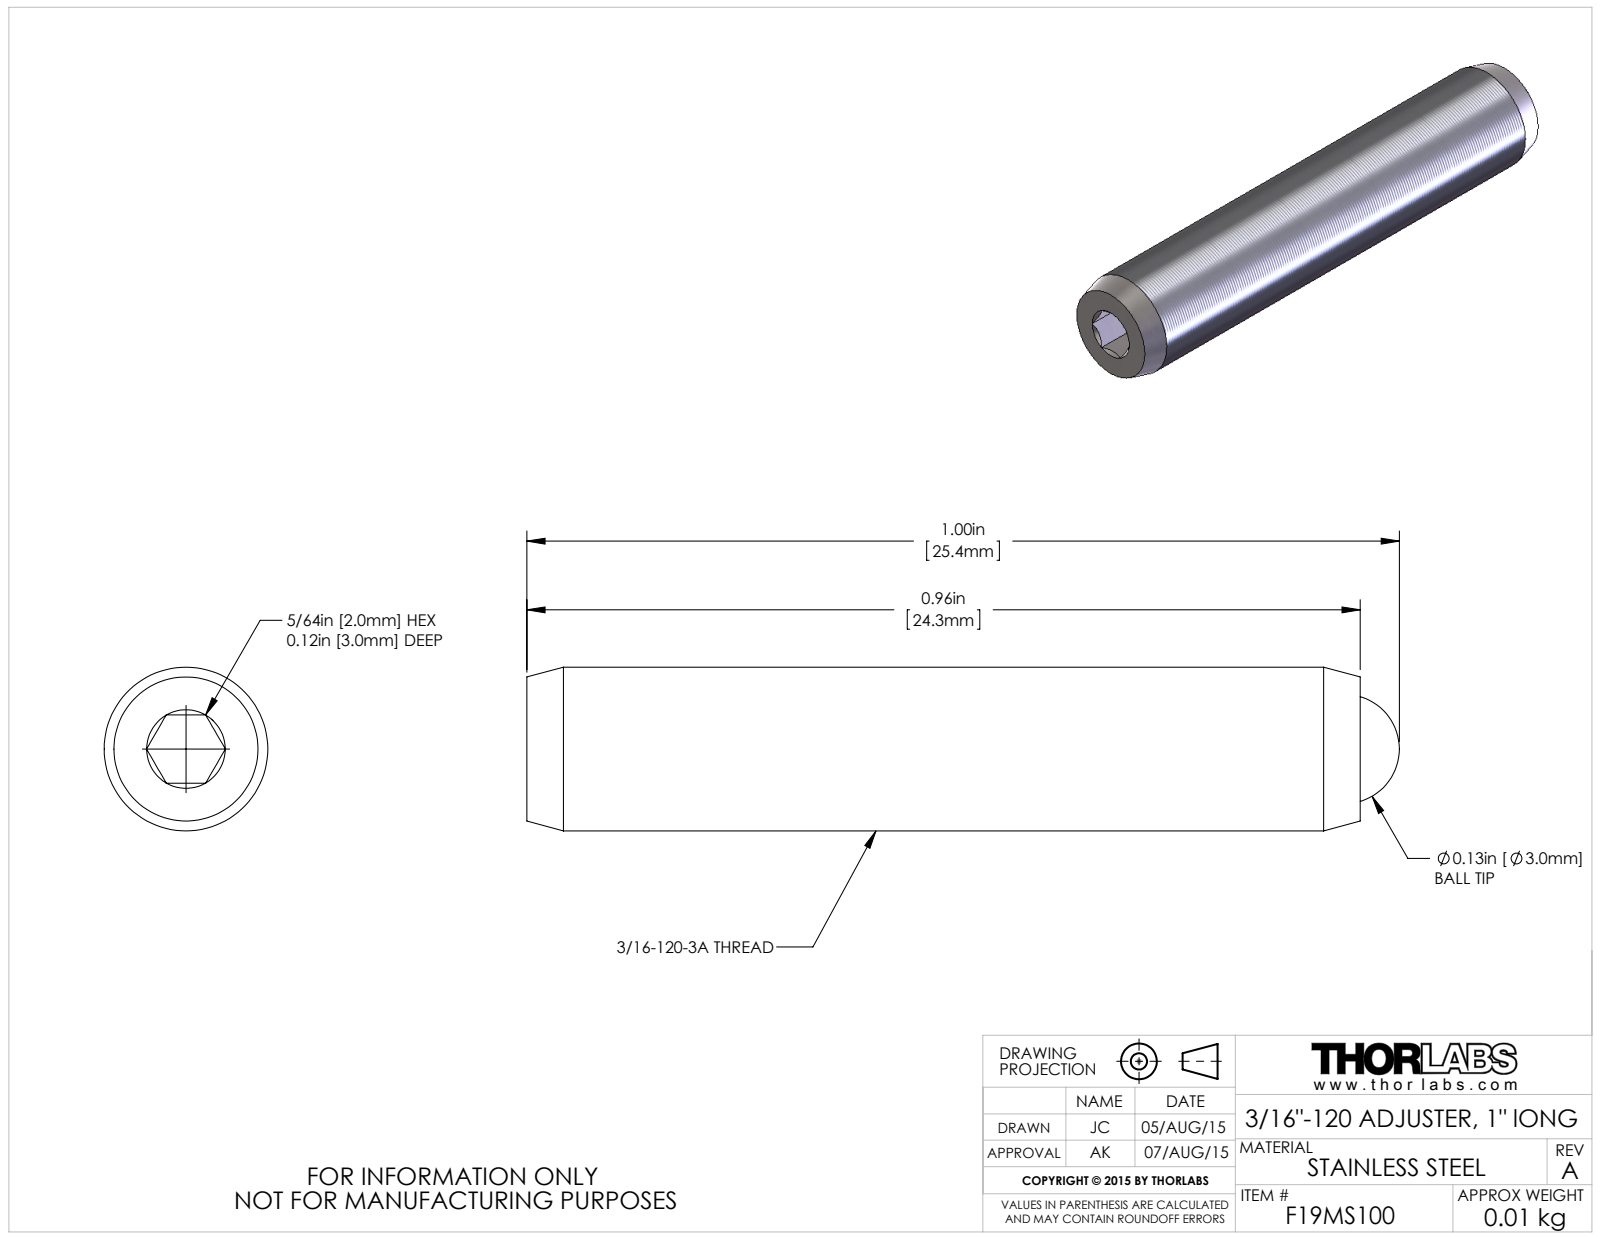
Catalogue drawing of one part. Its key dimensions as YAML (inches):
part_name: "TTN045706-E0W"
step_written_by: "SolidWorks 2014 (AUTOMOTIVE_DESIGN)"
units: inches
bodies: {solids: 2, faces: 29, planar: 9, cylindrical: 4, other: 16}
overall_size: [1, 0.188, 0.188]
volume: 0.026
surface_area: 0.707
round_holes:
  - {diameter: 0.126, count: 1}
round_bosses_or_shafts:
  - {diameter: 0.187, count: 1}
face_to_face_distances: [0.078, 0.955, 0.12, 0.835, 0.078]
